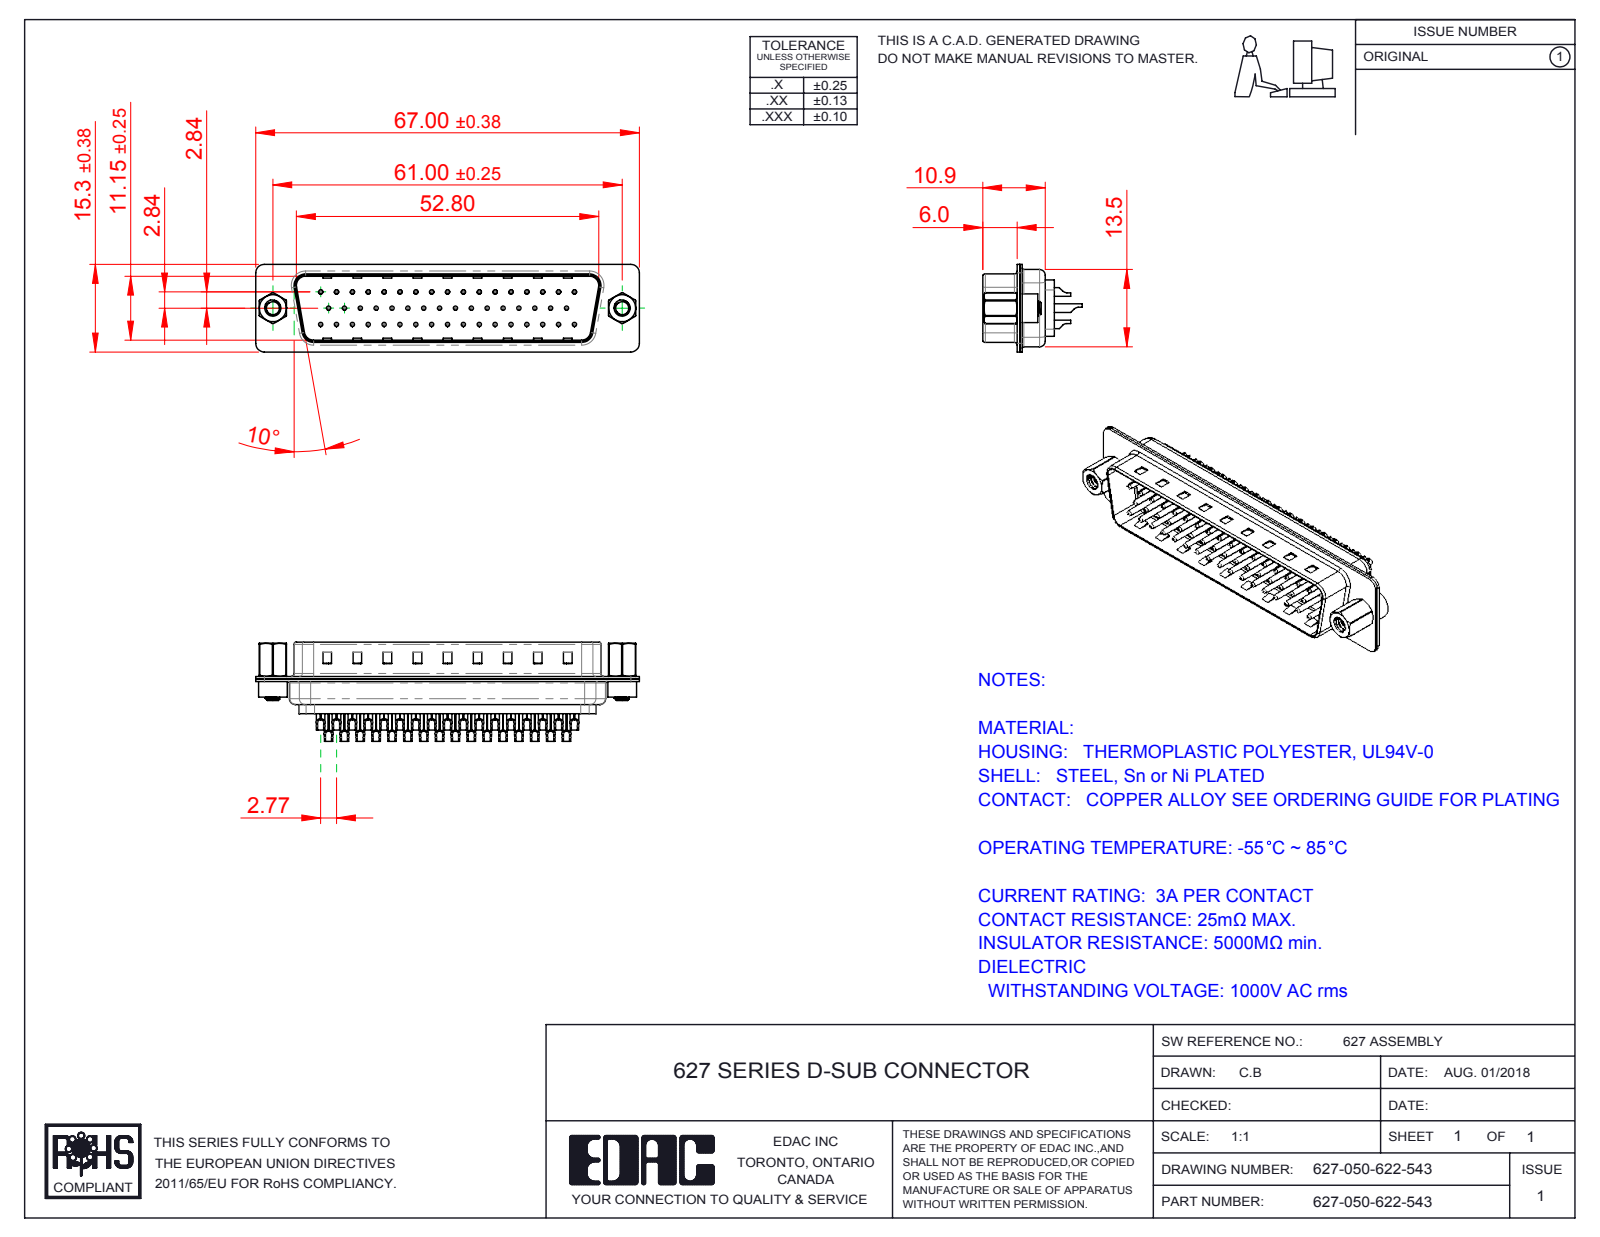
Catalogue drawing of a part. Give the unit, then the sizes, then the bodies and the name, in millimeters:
Units: millimetres
Overall size (bounding box): 67 × 17.35 × 15.3
Round holes (diameter × count): ⌀0.35 ×50, ⌀1.1 ×50, ⌀1.6 ×50, ⌀2.26 ×2, ⌀2.29 ×2, ⌀4 ×2, ⌀4.8 ×2
Round bosses / shafts (diameter × count): ⌀2 ×50, ⌀1.5 ×50, ⌀0.75 ×50, ⌀5 ×2, ⌀4.9 ×2, ⌀2.79 ×2
Partial cylindrical surfaces — rounded edges, fillets, slot ends (radius × count): R1.5 ×16, R2 ×12, R0.5 ×8, R1.6 ×8, R1 ×7, R0.25 ×4, R0.6 ×4, R0.65 ×4
Main face-to-face distances: 0.4, 0.45, 11.55, 0.9, 6.05, 6.5, 0.78, 12.33, 1.95, 0.77
Hole centre spacings: 3.16, 2.77, 5.54, 8.31, 11.08, 13.85, 16.62, 5.03
Volume: 4 682 mm³ · Surface area: 13 447 mm²
Bodies: 57 solids, 3738 faces (925 planar, 1663 cylindrical, 1150 other)
Part name (STEP PRODUCT): 627-050-622-543; 627 4-40 Hex Standoff; 627 4-40 Threaded Rivet; 627 Contact Row 3_22L (+5 more)
STEP written by: SolidWorks 2016 (CONFIG_CONTROL_DESIGN)
